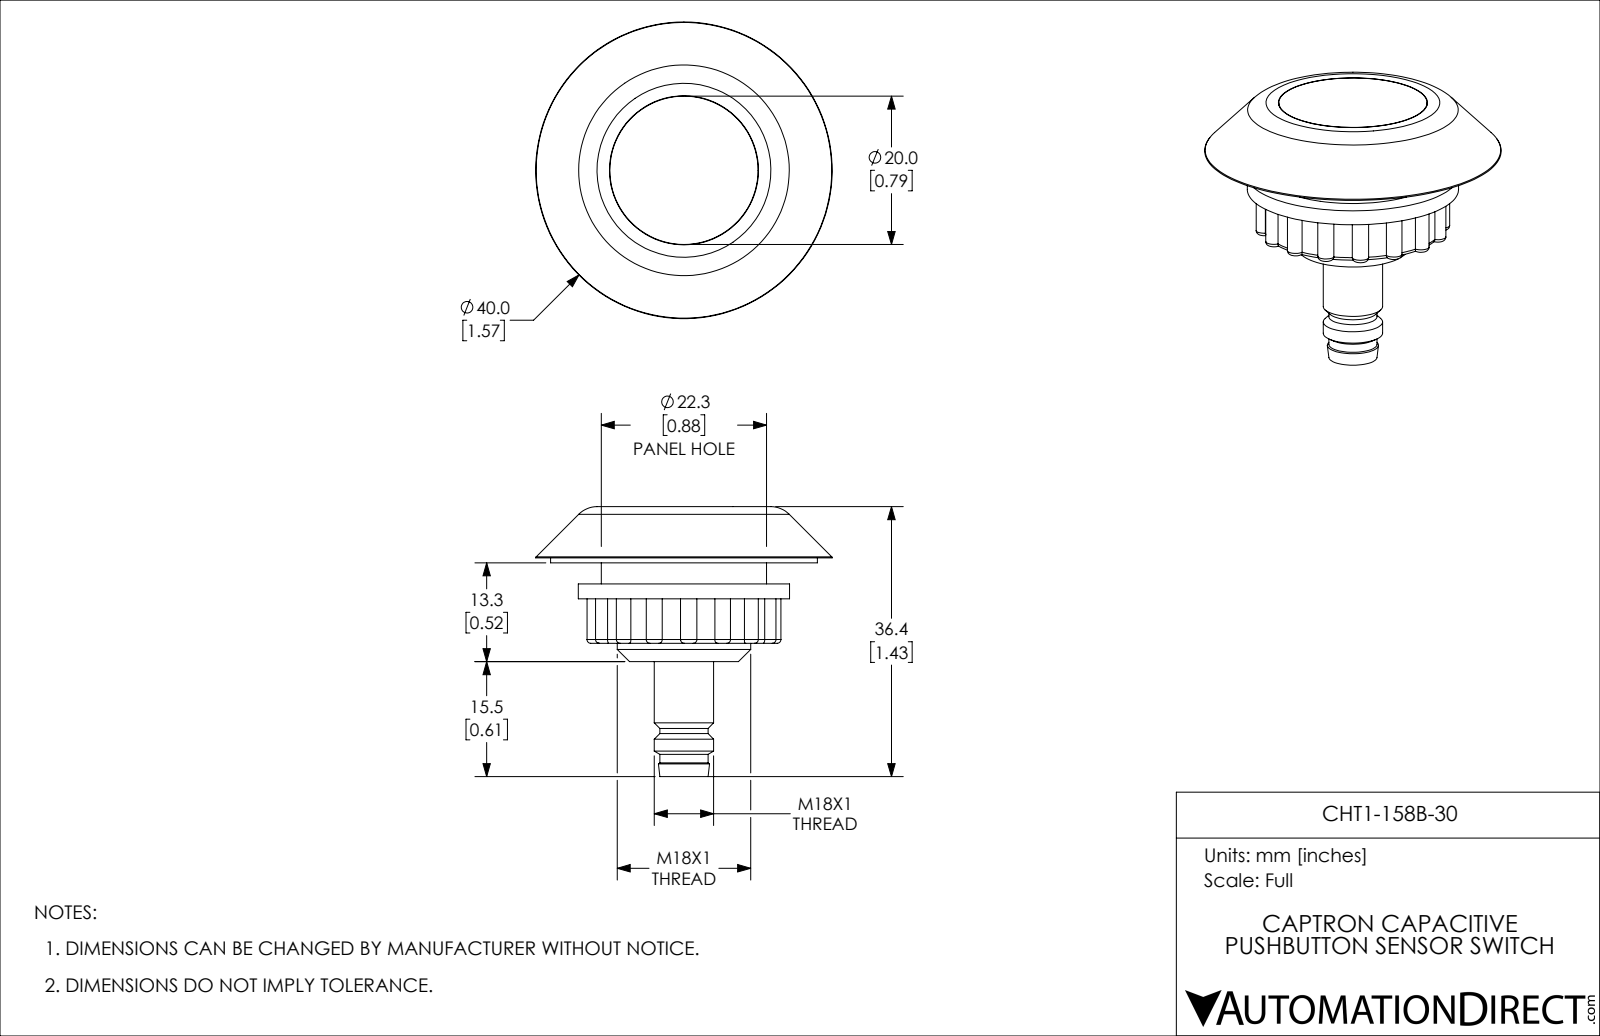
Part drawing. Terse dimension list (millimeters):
name: CHT1-158B-30
written by: SolidWorks 2019 (CONFIG_CONTROL_DESIGN)
unit: mm
bodies: 11 solids, 198 faces (26 planar, 92 cylindrical, 80 other)
size: 40 × 40 × 36.4
volume: 10 989 mm³; area: 10 253 mm²
holes: 1× ⌀14.7, 1× ⌀17, 1× ⌀20.1, 1× ⌀22.5, 1× ⌀22.6, 1× ⌀37
bosses: 5× ⌀1, 1× ⌀36, 1× ⌀28.5, 1× ⌀22.3, 1× ⌀18, 1× ⌀14.4, 1× ⌀8, 1× ⌀6.5
rounds: 16× R1.1, 1× R1, 1× R2.9, 1× R12
face distances: 6, 3, 1.57, 0.9, 7.57, 5.1, 6.67, 4.57, 2.1, 11.52
